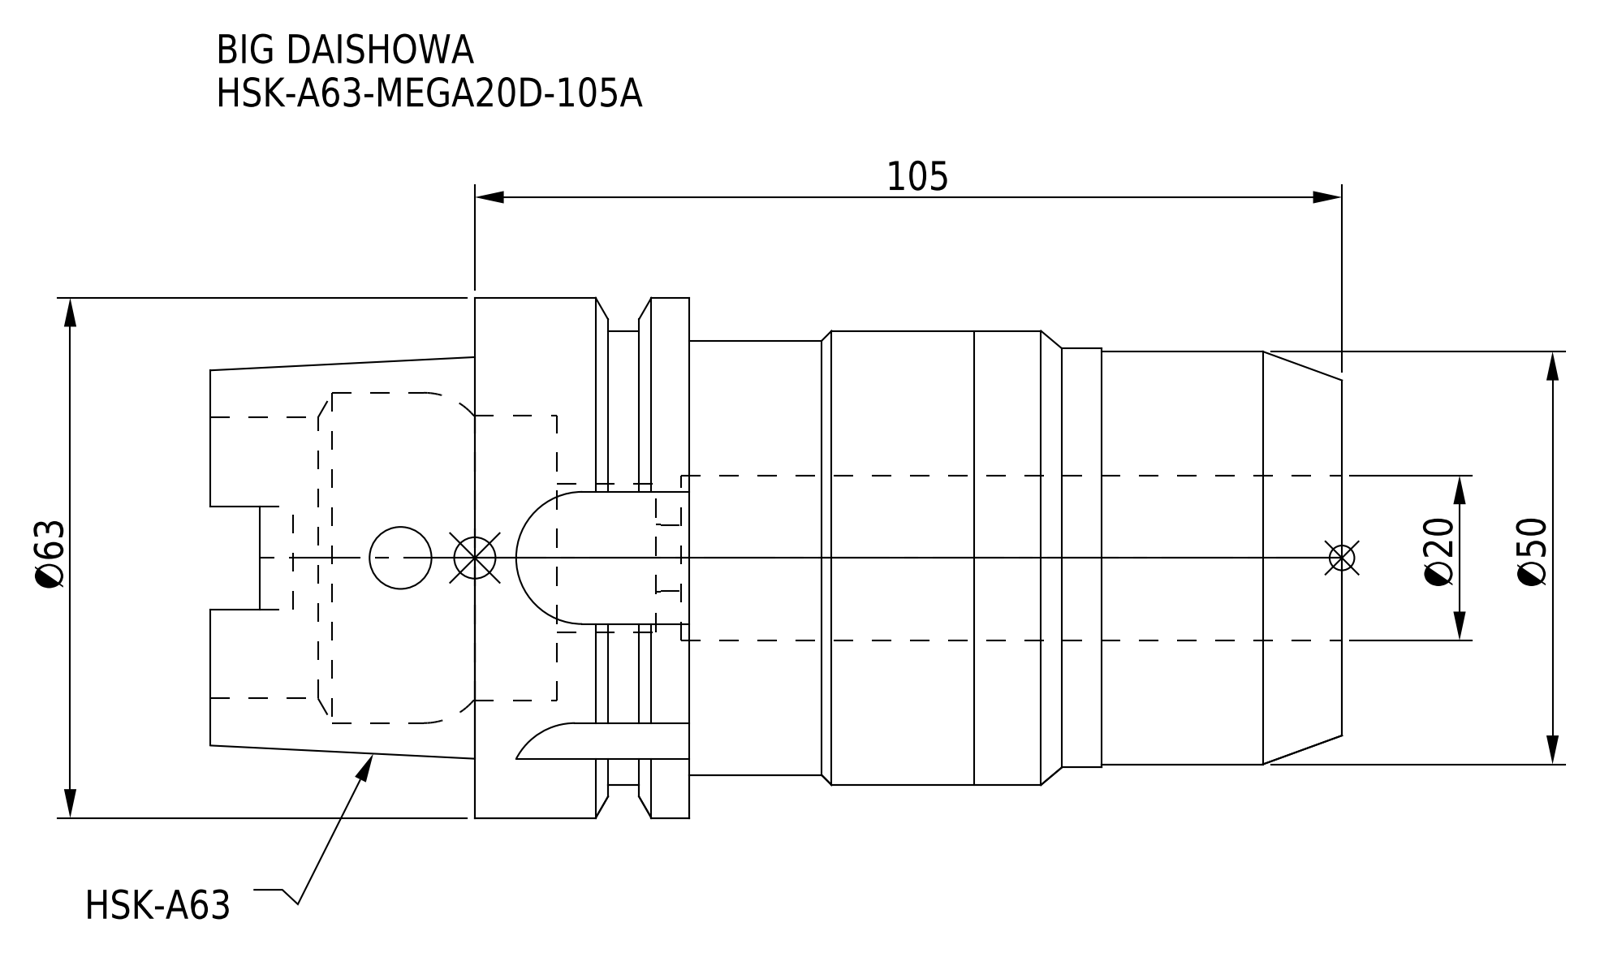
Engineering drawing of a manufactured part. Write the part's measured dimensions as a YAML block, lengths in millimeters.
part_name: "HSK-A63-MEGA20D-105A"
step_written_by: "CREO PARAMETRIC BY PTC INC, 2016380 (AUTOMOTIVE_DESIGN)"
units: millimeters
bodies: {solids: 1, faces: 102, planar: 39, cylindrical: 43, other: 20}
overall_size: [137, 63, 63]
volume: 224172
surface_area: 39839
round_holes:
  - {diameter: 7.5, count: 1}
  - {diameter: 8, count: 1}
  - {diameter: 8.2, count: 1}
  - {diameter: 18, count: 1}
  - {diameter: 20, count: 1}
  - {diameter: 34, count: 1}
  - {diameter: 34.5, count: 1}
  - {diameter: 40, count: 1}
round_bosses_or_shafts:
  - {diameter: 63, count: 1}
  - {diameter: 55, count: 1}
  - {diameter: 52.6, count: 1}
  - {diameter: 50.7, count: 1}
  - {diameter: 50, count: 1}
partial_cylinders:
  - {radius: 2.88, count: 4}
  - {radius: 8, count: 4}
face_to_face_distances: [105, 26, 79, 95.05, 16.05, 9.95, 137, 58, 41.95, 32]
